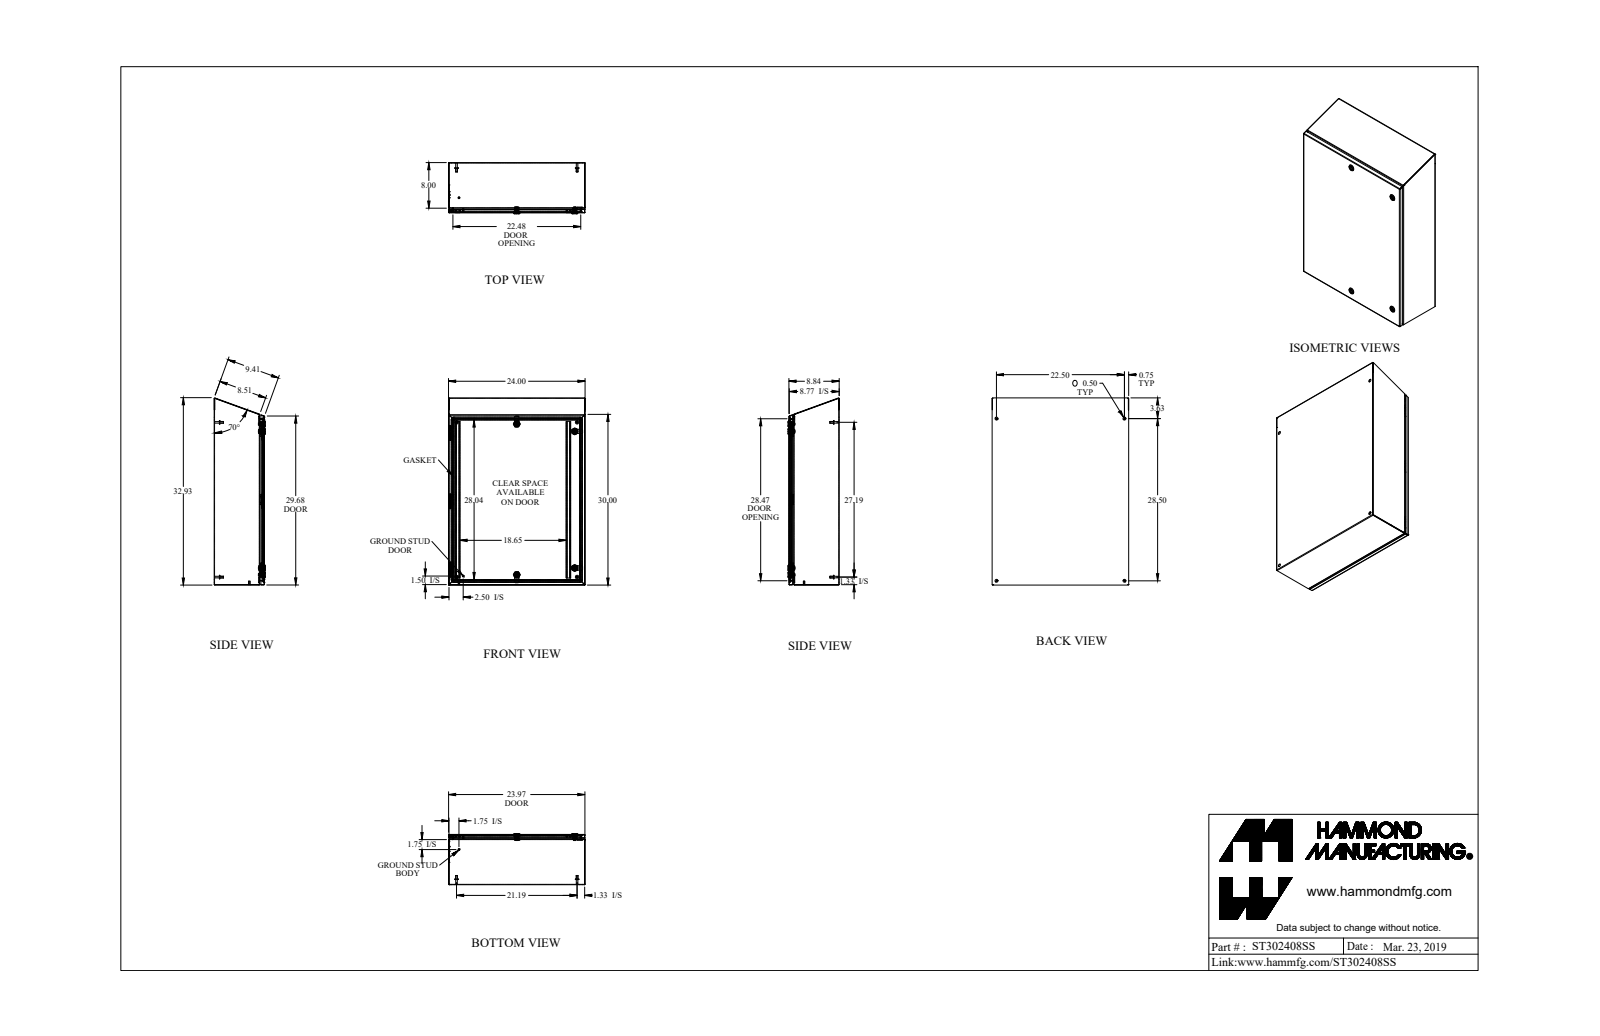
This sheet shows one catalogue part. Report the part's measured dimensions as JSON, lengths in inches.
{"part_name": "ST302408SS", "step_written_by": "SolidWorks 2018 (AUTOMOTIVE_DESIGN)", "units": "inches", "bodies": {"solids": 43, "faces": 1146, "planar": 632, "cylindrical": 346, "other": 168}, "overall_size": [32.883, 24, 8.997], "volume_in3": 204.2, "surface_area_in2": 5718, "round_holes": [[0.5, 8], [0.197, 4], [0.387, 4], [0.63, 4], [0.768, 4], [0.172, 1], [0.24, 1], [0.242, 1]], "round_bosses_or_shafts": [[0.625, 8], [0.313, 6], [1.1, 4], [0.525, 4], [0.275, 4], [0.236, 4], [0.785, 2], [0.785, 2]], "partial_cylinders_radius": [[0.036, 20], [0.108, 20], [0.01, 12], [0.048, 12], [0.25, 11], [0.125, 8], [0.006, 6], [0.062, 6]], "face_to_face_distances": [0.072, 8.765, 8.693, 8.837, 23.928, 23.856, 24, 7.928, 0.837, 0.038], "hole_center_spacings": [2.493, 21.544, 22.5, 26.272, 28.5, 33.884, 36.311, 10.258]}
